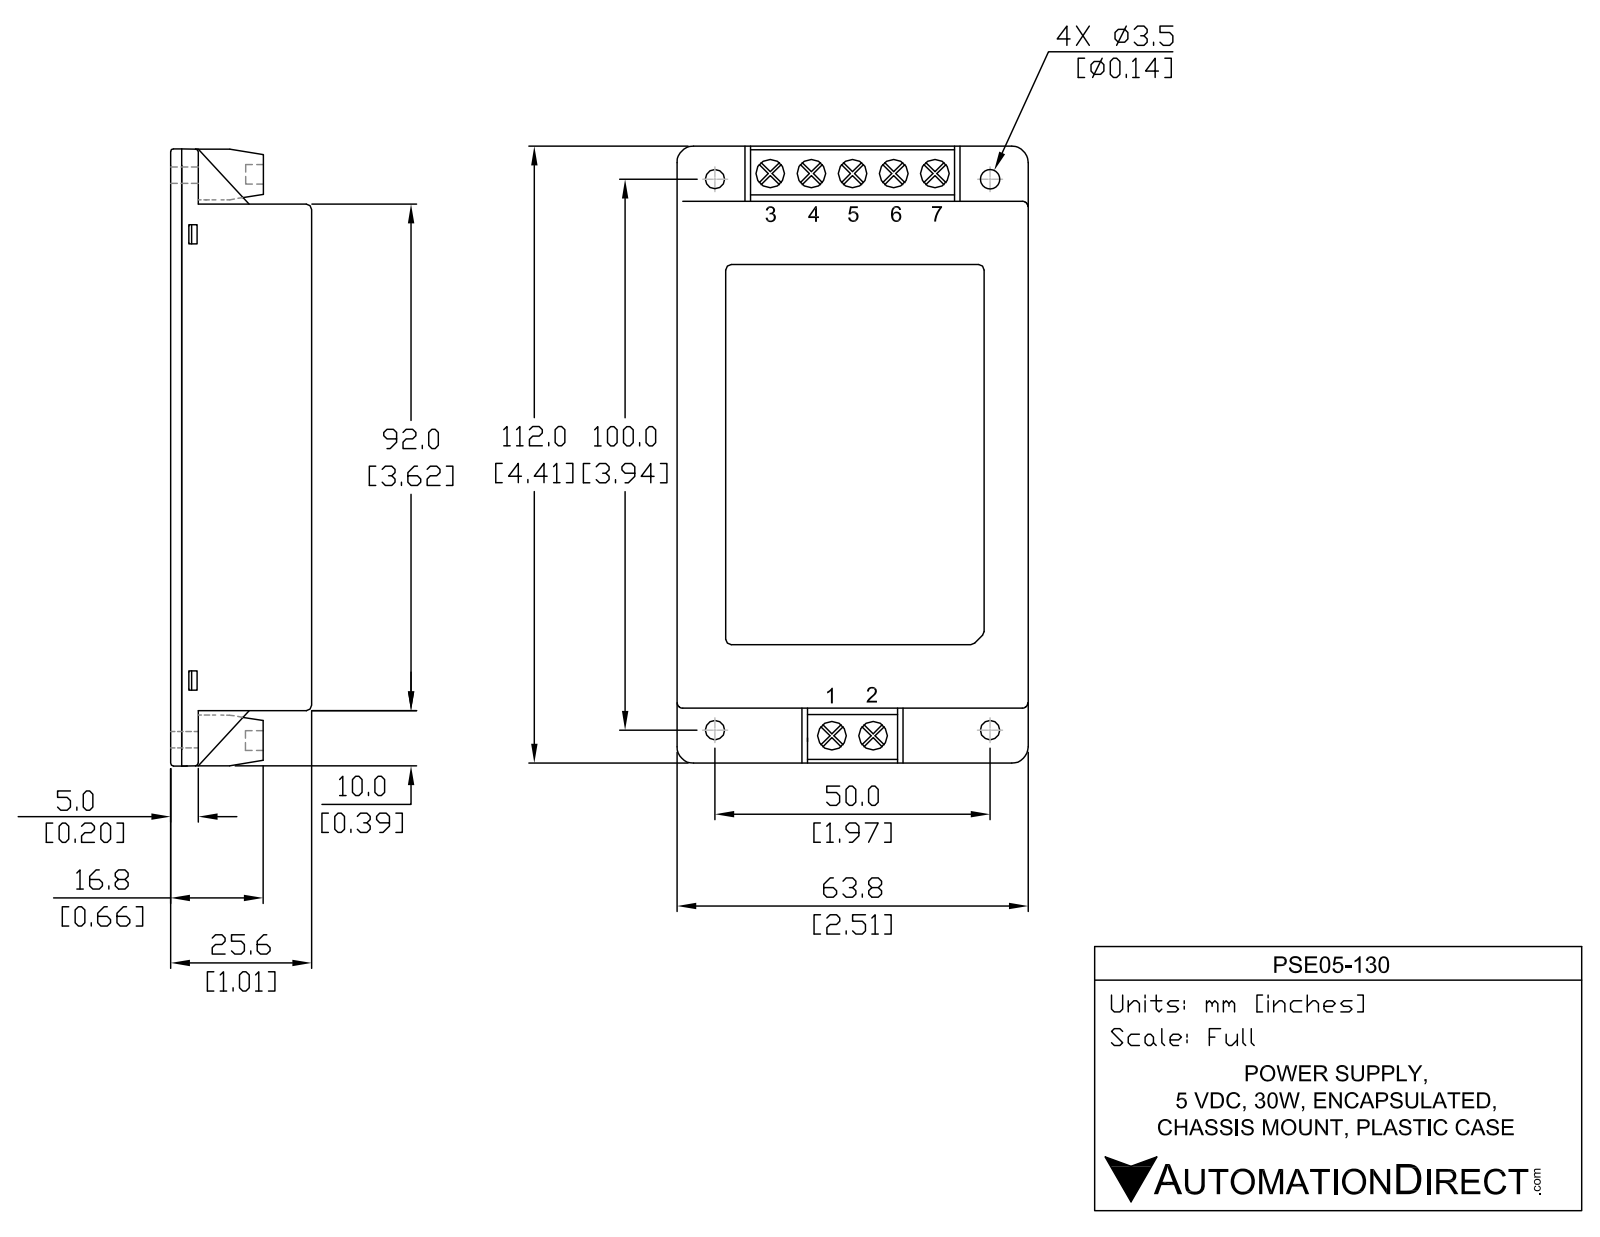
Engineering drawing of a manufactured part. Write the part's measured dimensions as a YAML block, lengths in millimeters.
part_name: "PSE05-130"
step_written_by: "SolidWorks 2011 (CONFIG_CONTROL_DESIGN)"
units: millimeters
bodies: {solids: 2, faces: 374, planar: 246, cylindrical: 62, other: 66}
overall_size: [112, 63.8, 25.7]
volume: 161200
surface_area: 39030
round_holes:
  - {diameter: 5.1, count: 7}
  - {diameter: 3.6, count: 4}
partial_cylinders:
  - {radius: 0.8, count: 20}
  - {radius: 3.2, count: 4}
face_to_face_distances: [2, 2, 23.6, 25.6, 23.6, 25.7, 23.7, 63.8, 91.9, 0.4]
hole_center_spacings: [6.6, 13.2, 6.6, 21.7, 28.3, 50, 100.1, 102]
